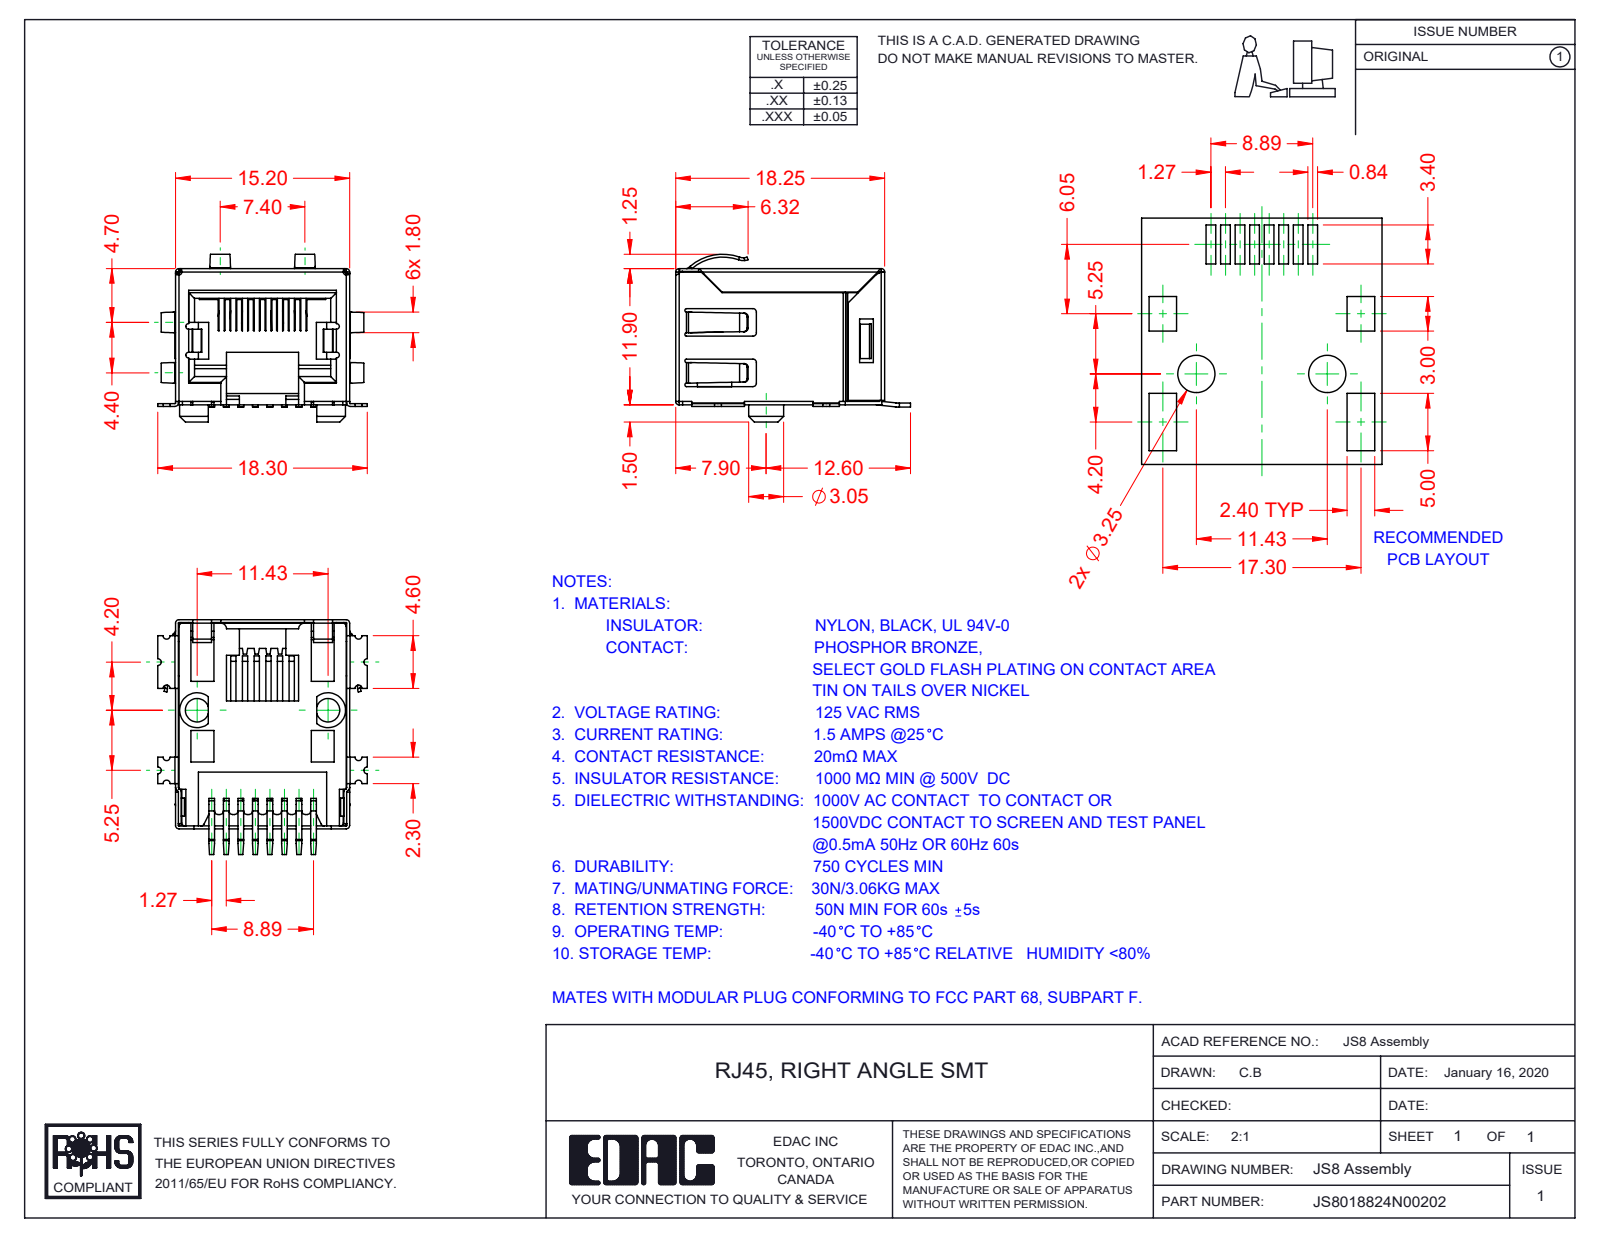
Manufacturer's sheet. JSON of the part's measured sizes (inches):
{"part_name": "S8 Contacts; S8 Shield; S8 Insulator; RJS8018824N00202", "step_written_by": "SolidWorks 2016 (CONFIG_CONTROL_DESIGN)", "units": "inches", "bodies": {"solids": 10, "faces": 976, "planar": 602, "cylindrical": 314, "other": 60}, "overall_size": [0.807, 0.72, 0.577], "volume_in3": 0.08, "surface_area_in2": 7.183, "partial_cylinders_radius": [[0.012, 59], [0.01, 19], [0.02, 18], [0.008, 17], [0.006, 8], [0.03, 7], [0.039, 4], [0.049, 3]], "face_to_face_distances": [0.577, 0.589, 0.587, 0.039, 0.014, 0.579, 0.03, 0.429, 0.043, 0.598]}
